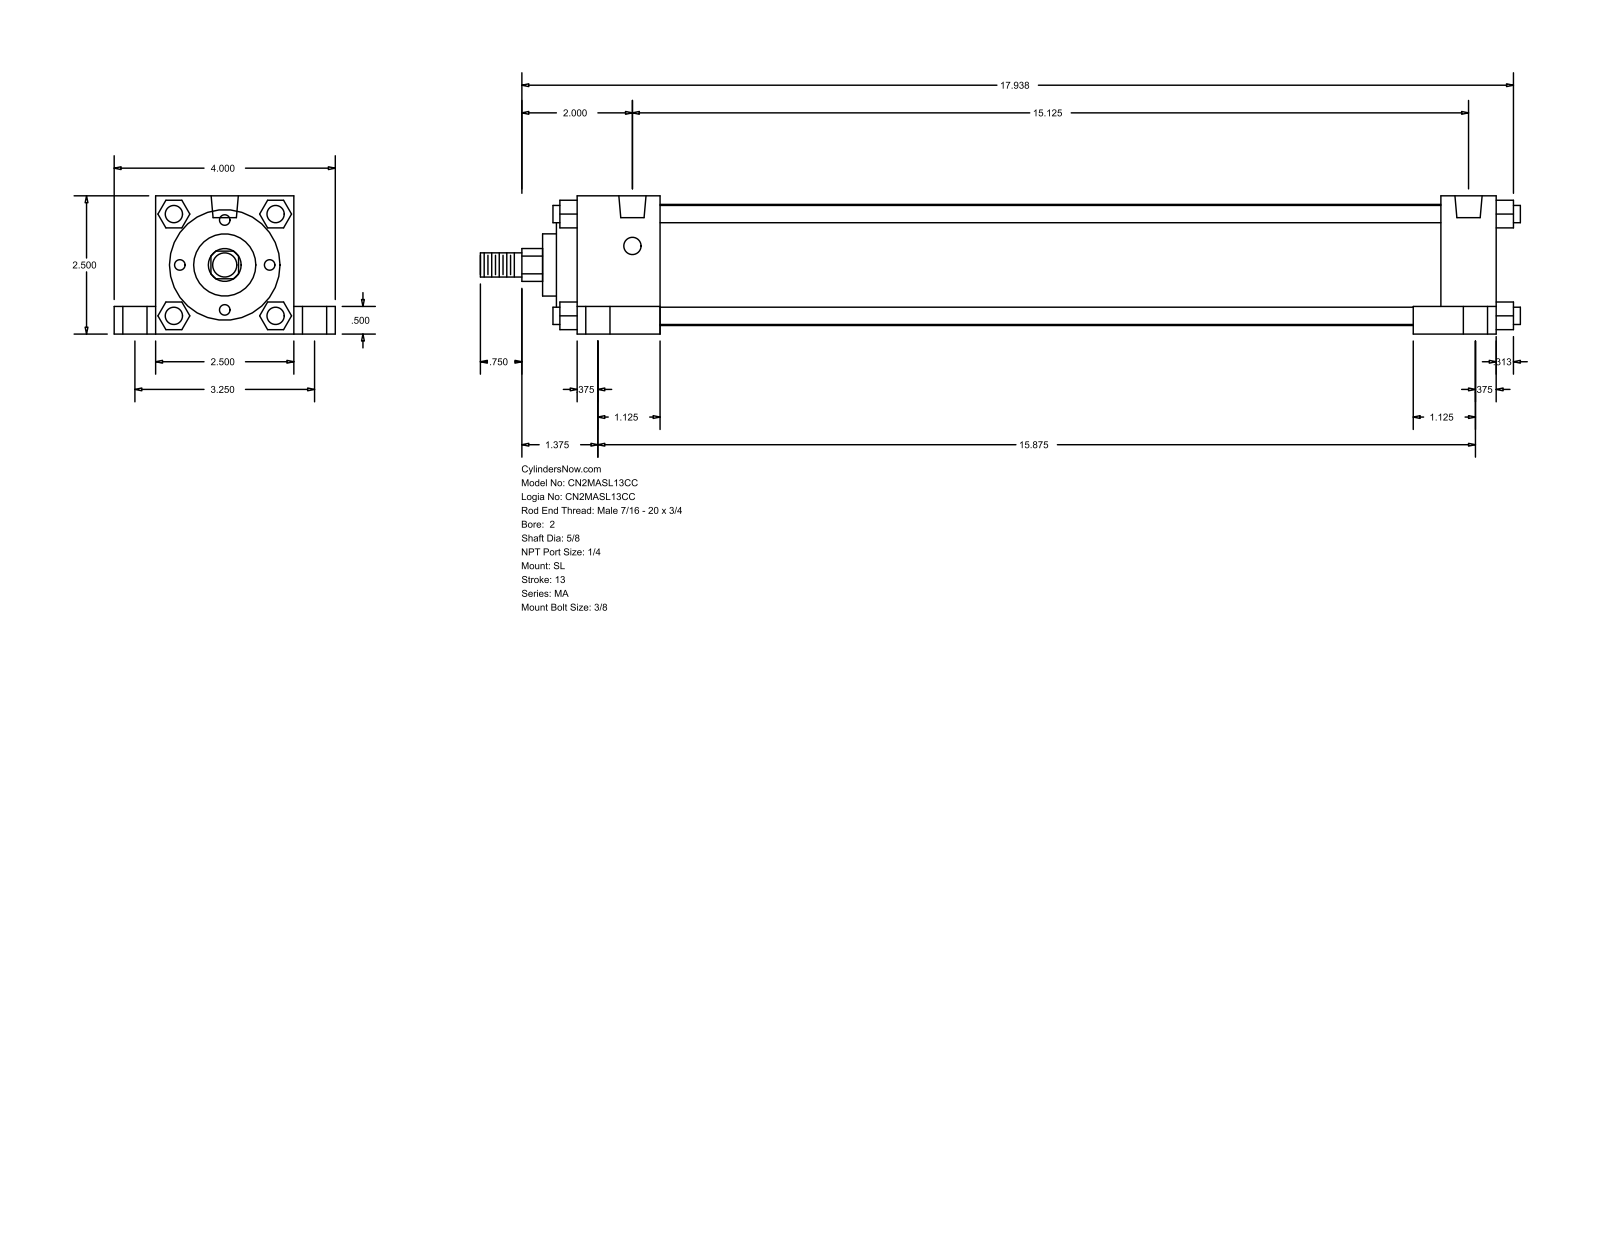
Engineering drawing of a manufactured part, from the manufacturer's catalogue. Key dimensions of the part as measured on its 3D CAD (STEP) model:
Part name (STEP PRODUCT): MA_SL__0200_0.625
STEP written by: GSSL Pune (CONFIG_CONTROL_DESIGN)
Units: millimetres
Bodies: 0 solids, 150 faces (113 planar, 37 cylindrical, 0 other)
Overall size (bounding box): 477.84 × 101.6 × 63.5
Round holes (diameter × count): ⌀7.94 ×4, ⌀11.11 ×4, ⌀17.46 ×4, ⌀12.49 ×2
Round bosses / shafts (diameter × count): ⌀7.94 ×4, ⌀55.63 ×1, ⌀50.8 ×1, ⌀28.57 ×1, ⌀15.88 ×1, ⌀11.11 ×1
Partial cylindrical surfaces — rounded edges, fillets, slot ends (radius × count): R7.54 ×1
Main face-to-face distances: 63.5, 12.7, 9.52, 358.77, 19.05, 82.55, 38.1, 50.8, 422.28, 384.18
Hole centre spacings: 41.39, 44.22, 82.54, 384.18, 389.54, 402.18, 403.23, 411.59
